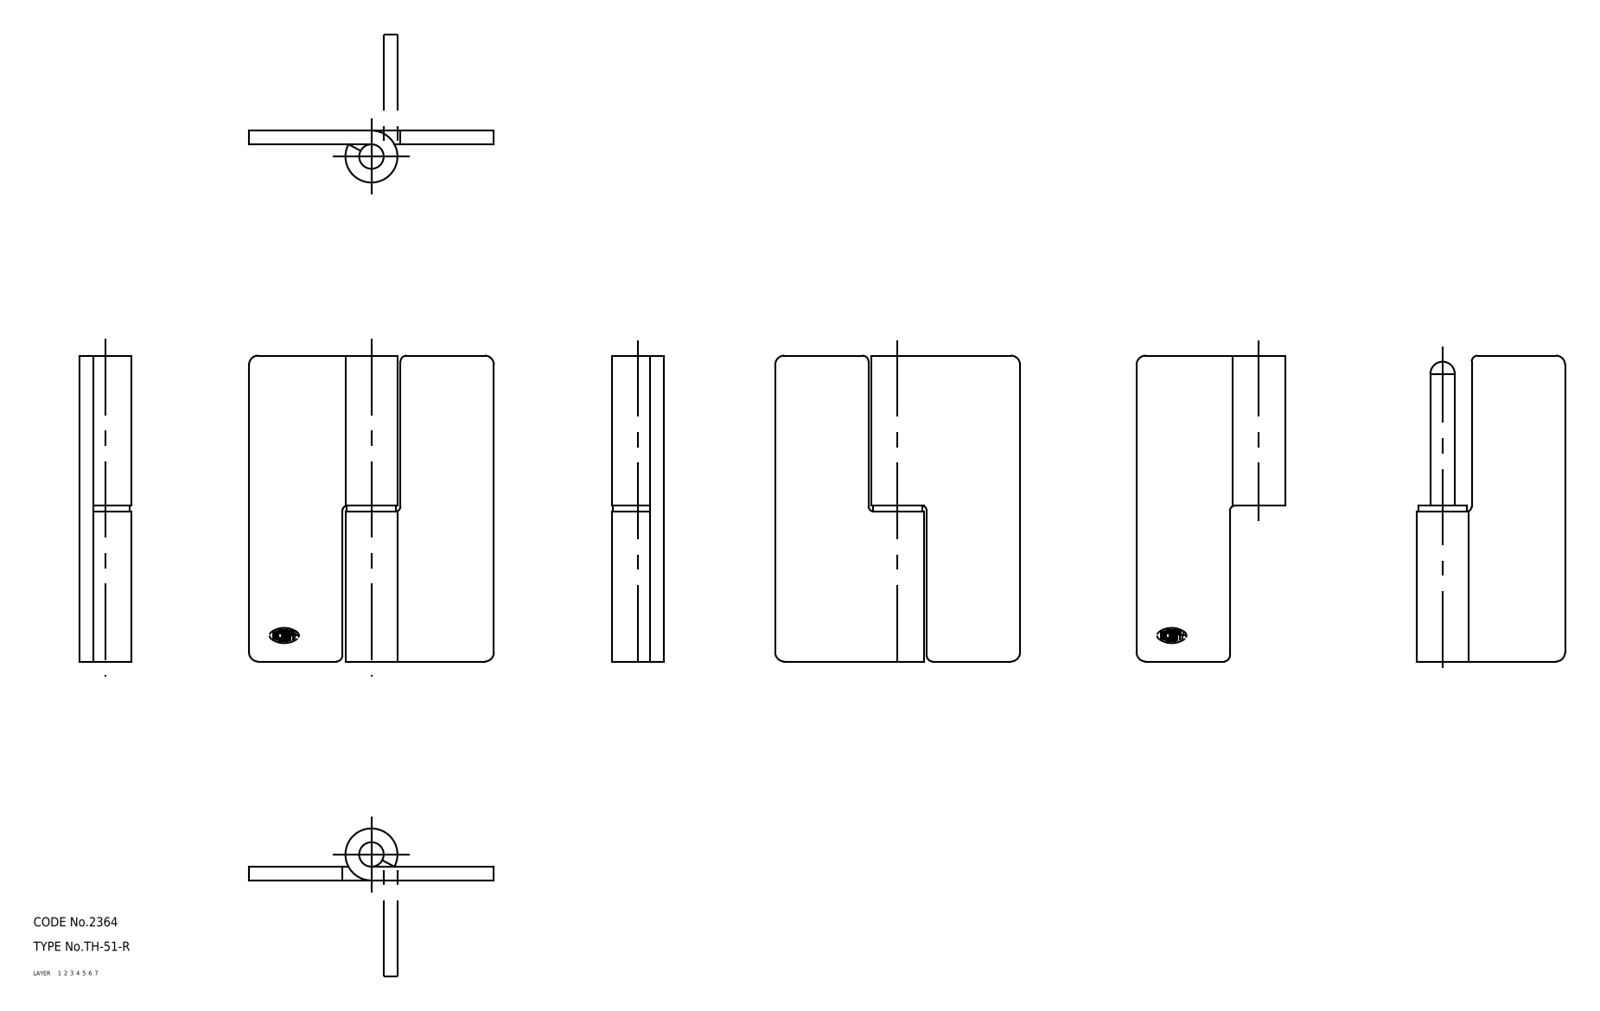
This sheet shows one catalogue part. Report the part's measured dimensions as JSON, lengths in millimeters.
{"part_name": "washer; shaft; hinge piece_B; hinge piece_A (+1 more)", "step_written_by": "CADfix (AUTOMOTIVE_DESIGN)", "units": "millimeters", "bodies": {"solids": 4, "faces": 36, "planar": 0, "cylindrical": 0, "other": 36}, "overall_size": [100, 80, 17], "volume_mm3": 51086, "surface_area_mm2": 26448}
